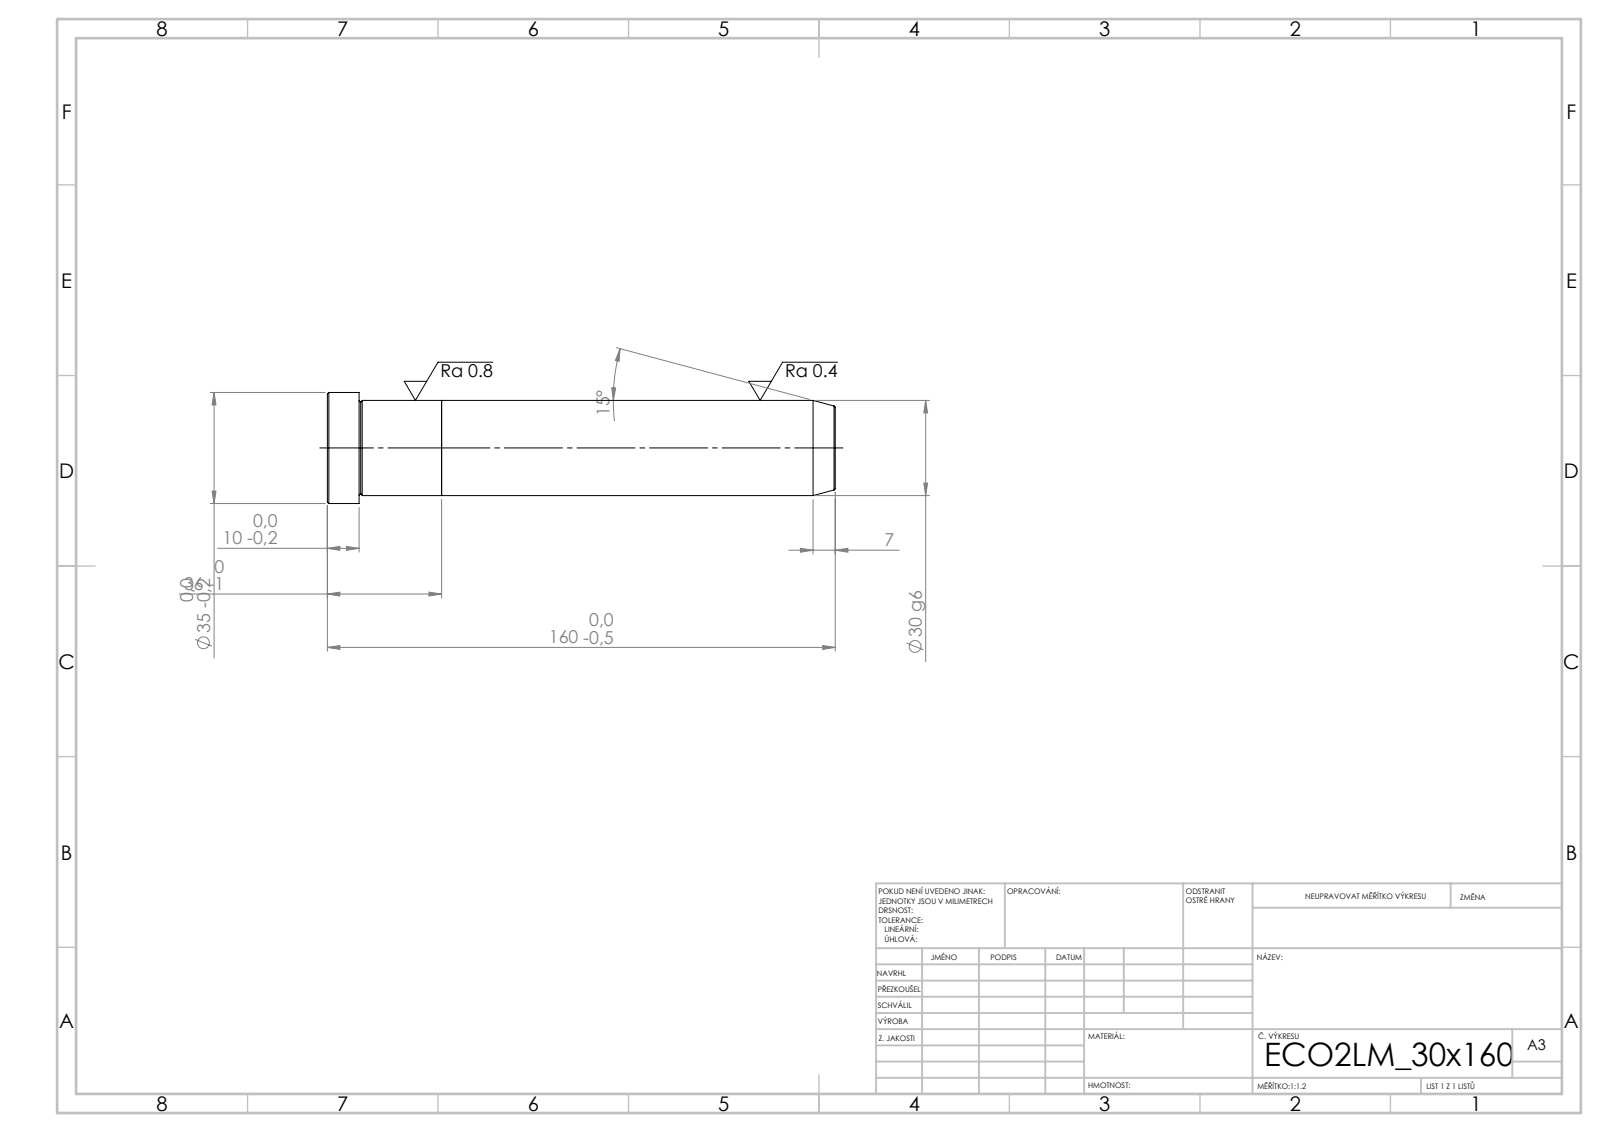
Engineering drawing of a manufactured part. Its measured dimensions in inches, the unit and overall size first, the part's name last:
Units: inches
Overall size (bounding box): 6.299 × 1.378 × 1.378
Round bosses / shafts (diameter × count): ⌀1.378 ×1, ⌀1.181 ×1
Main face-to-face distances: 1.417, 4.882, 6.299, 5.906, 1.024, 0.394
Volume: 7.018 in³ · Surface area: 28.52 in²
Bodies: 2 solids, 21 faces (5 planar, 6 cylindrical, 10 other)
STEP written by: SolidWorks 2019 (CONFIG_CONTROL_DESIGN)
